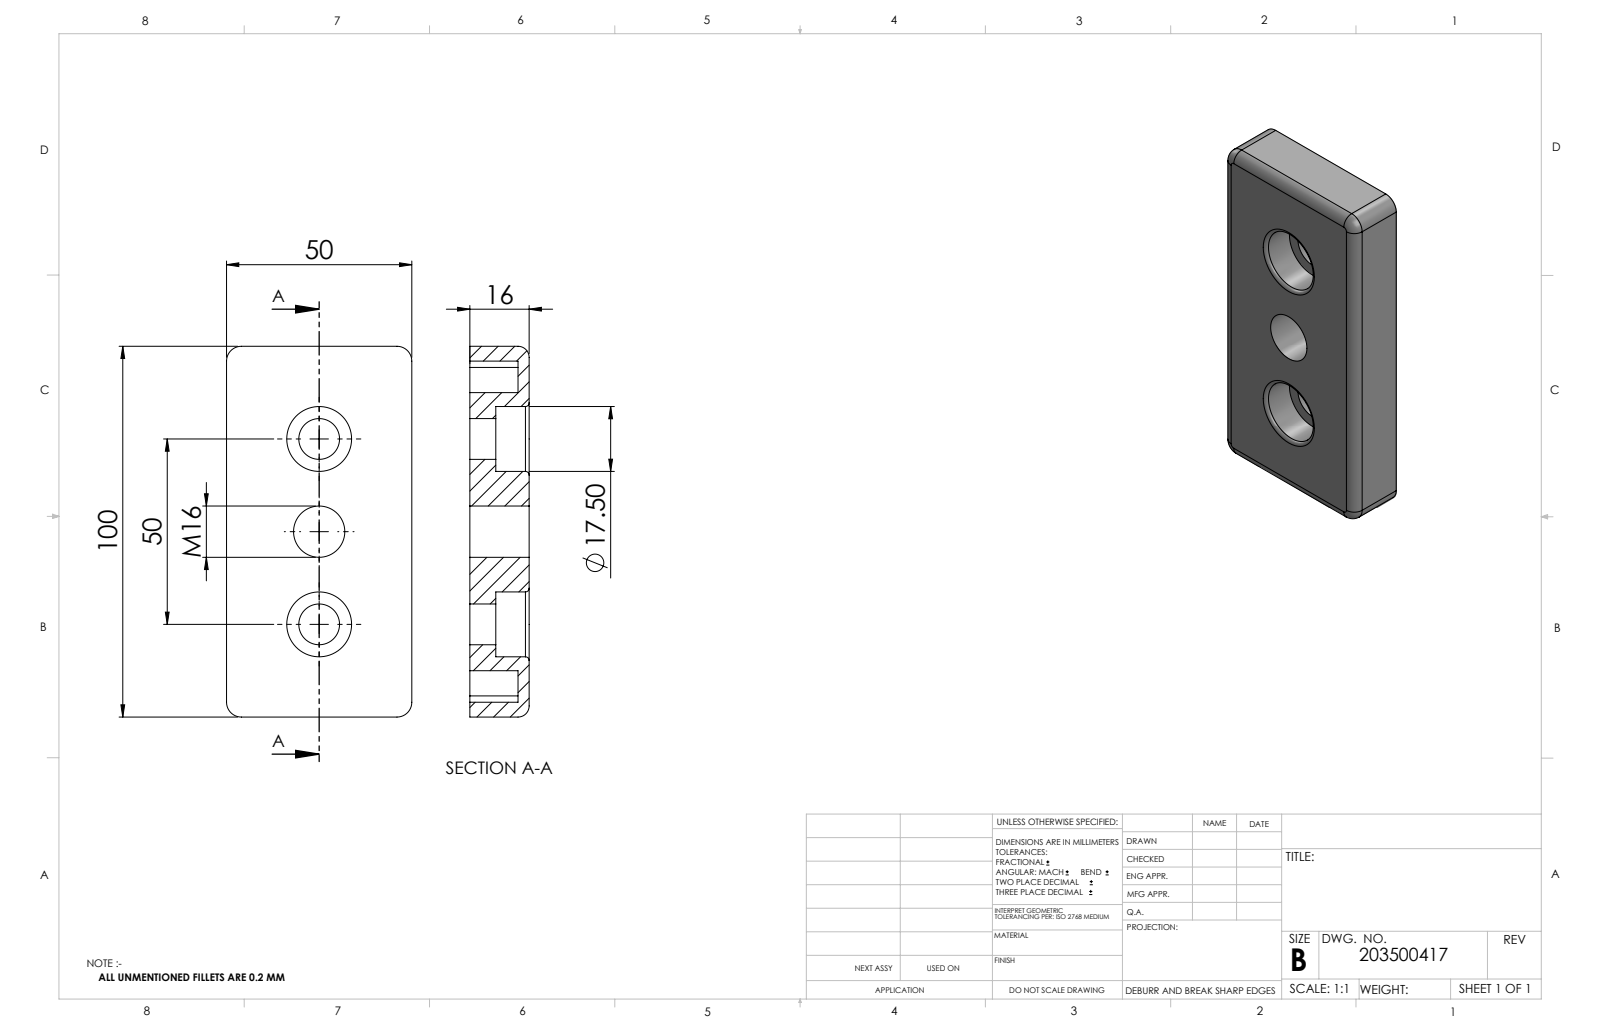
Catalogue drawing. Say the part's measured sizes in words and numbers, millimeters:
The part is named "203500417_c_1". Its 3-D file was written by "SolidWorks 2014 (CONFIG_CONTROL_DESIGN)". It is 1 solid with 104 faces: 32 planar, 64 cylindrical and 8 other. Overall it measures 100 by 50 by 16 millimeters. Its volume is 46 735 cubic millimeters and its surface area 22 537 square millimeters. Round holes: 2 of diameter 11, 2 of diameter 17.5, 1 of diameter 13.84. Partial cylindrical surfaces (rounded edges, fillets, slot ends): 28 of radius 1, 4 of radius 3, 4 of radius 4, 2 of radius 12.5, 1 of radius 14. The main face-to-face distances are 16, 4, 46, 13, 3, 50, 42, 96, 4.99, 35.35. The hole center spacings are 25, 50.
